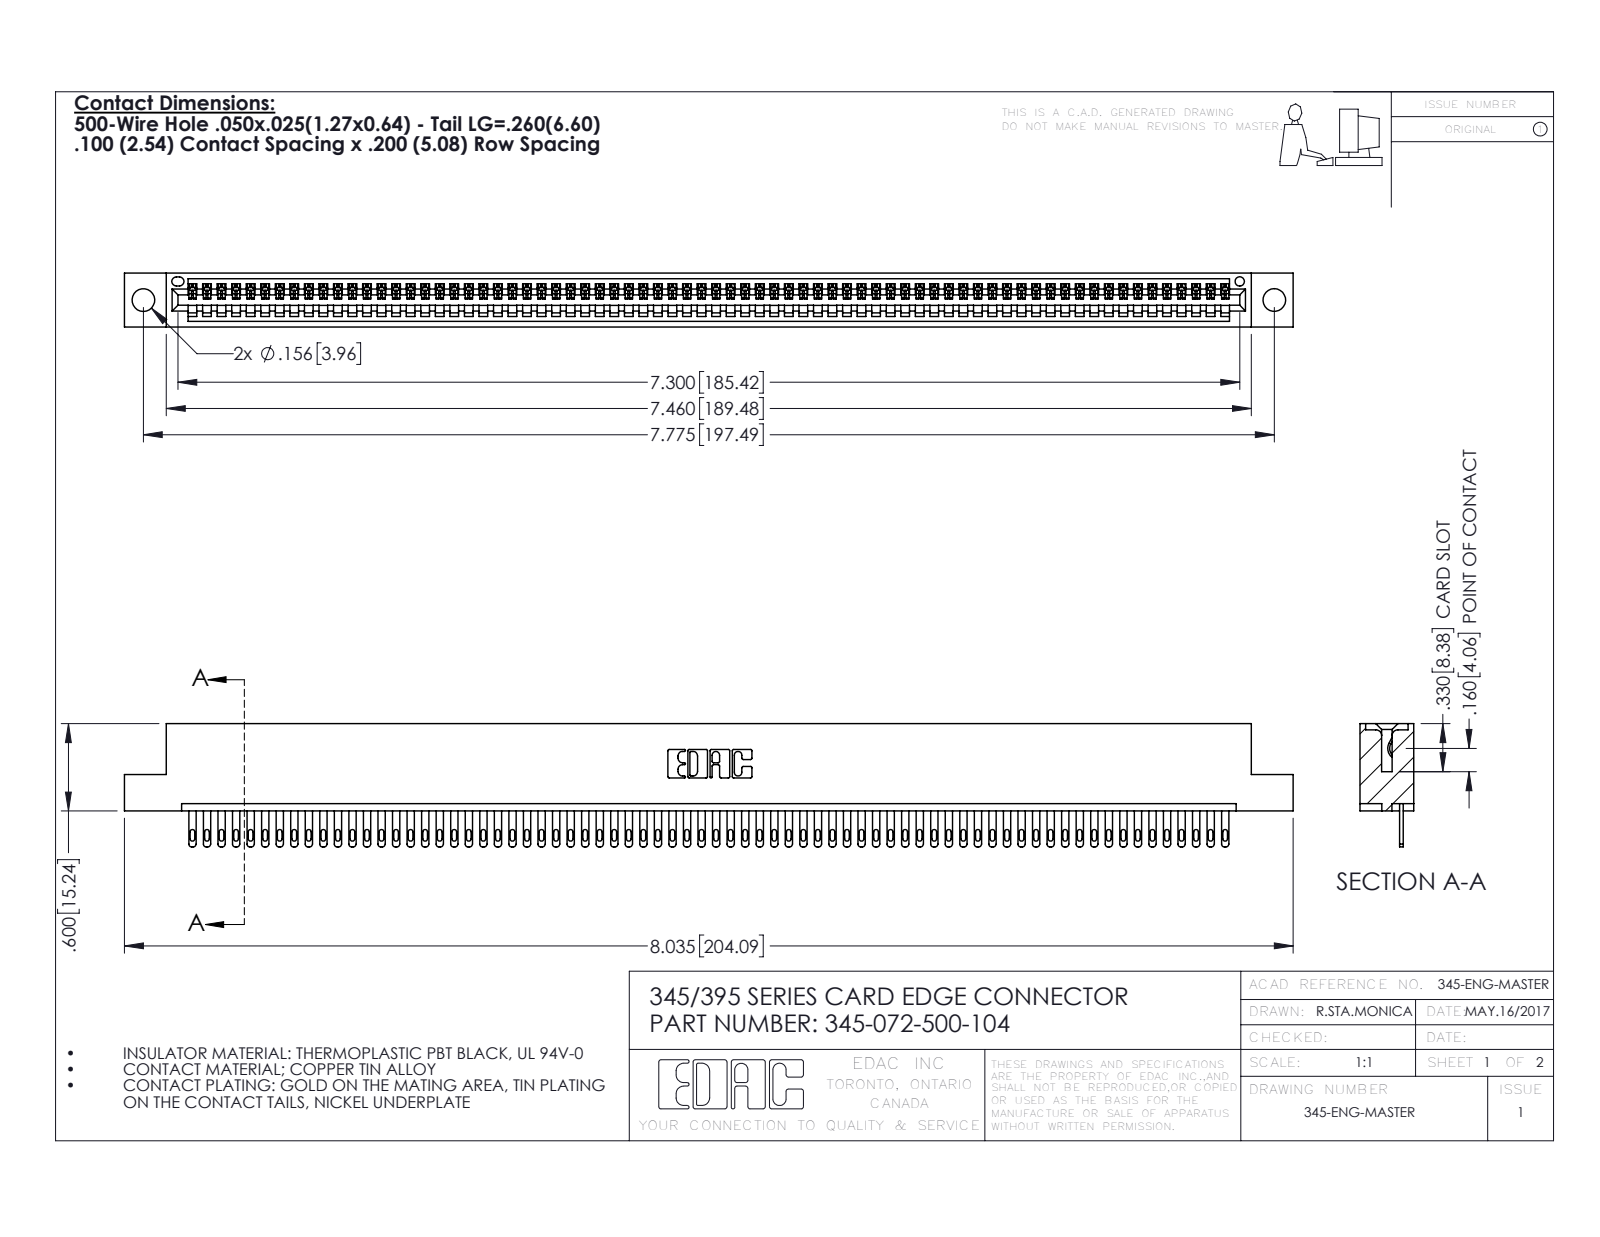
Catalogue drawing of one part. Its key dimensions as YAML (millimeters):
part_name: "345 Part_Flush Mounting Lugs - 0.156 Dia-TH; 345-292-001_345-293-100; 345-072-500-104"
step_written_by: "SolidWorks 2016 (CONFIG_CONTROL_DESIGN)"
units: millimeters
bodies: {solids: 73, faces: 4014, planar: 2528, cylindrical: 1486, other: 0}
overall_size: [204.1, 21.5, 9.4]
volume: 19580
surface_area: 26410
round_holes:
  - {diameter: 4, count: 2}
  - {diameter: 1.6, count: 1}
partial_cylinders:
  - {radius: 0.2, count: 144}
  - {radius: 0.4, count: 144}
  - {radius: 0.5, count: 144}
  - {radius: 0.3, count: 22}
  - {radius: 0.2, count: 6}
  - {radius: 0.8, count: 6}
  - {radius: 0.7, count: 3}
  - {radius: 0.8, count: 2}
face_to_face_distances: [7.6, 1.8, 9.4, 2.5, 6.9, 0.6, 5.1, 5.7, 3.8, 1.8]
hole_center_spacings: [6.9, 191.5, 197.5]
